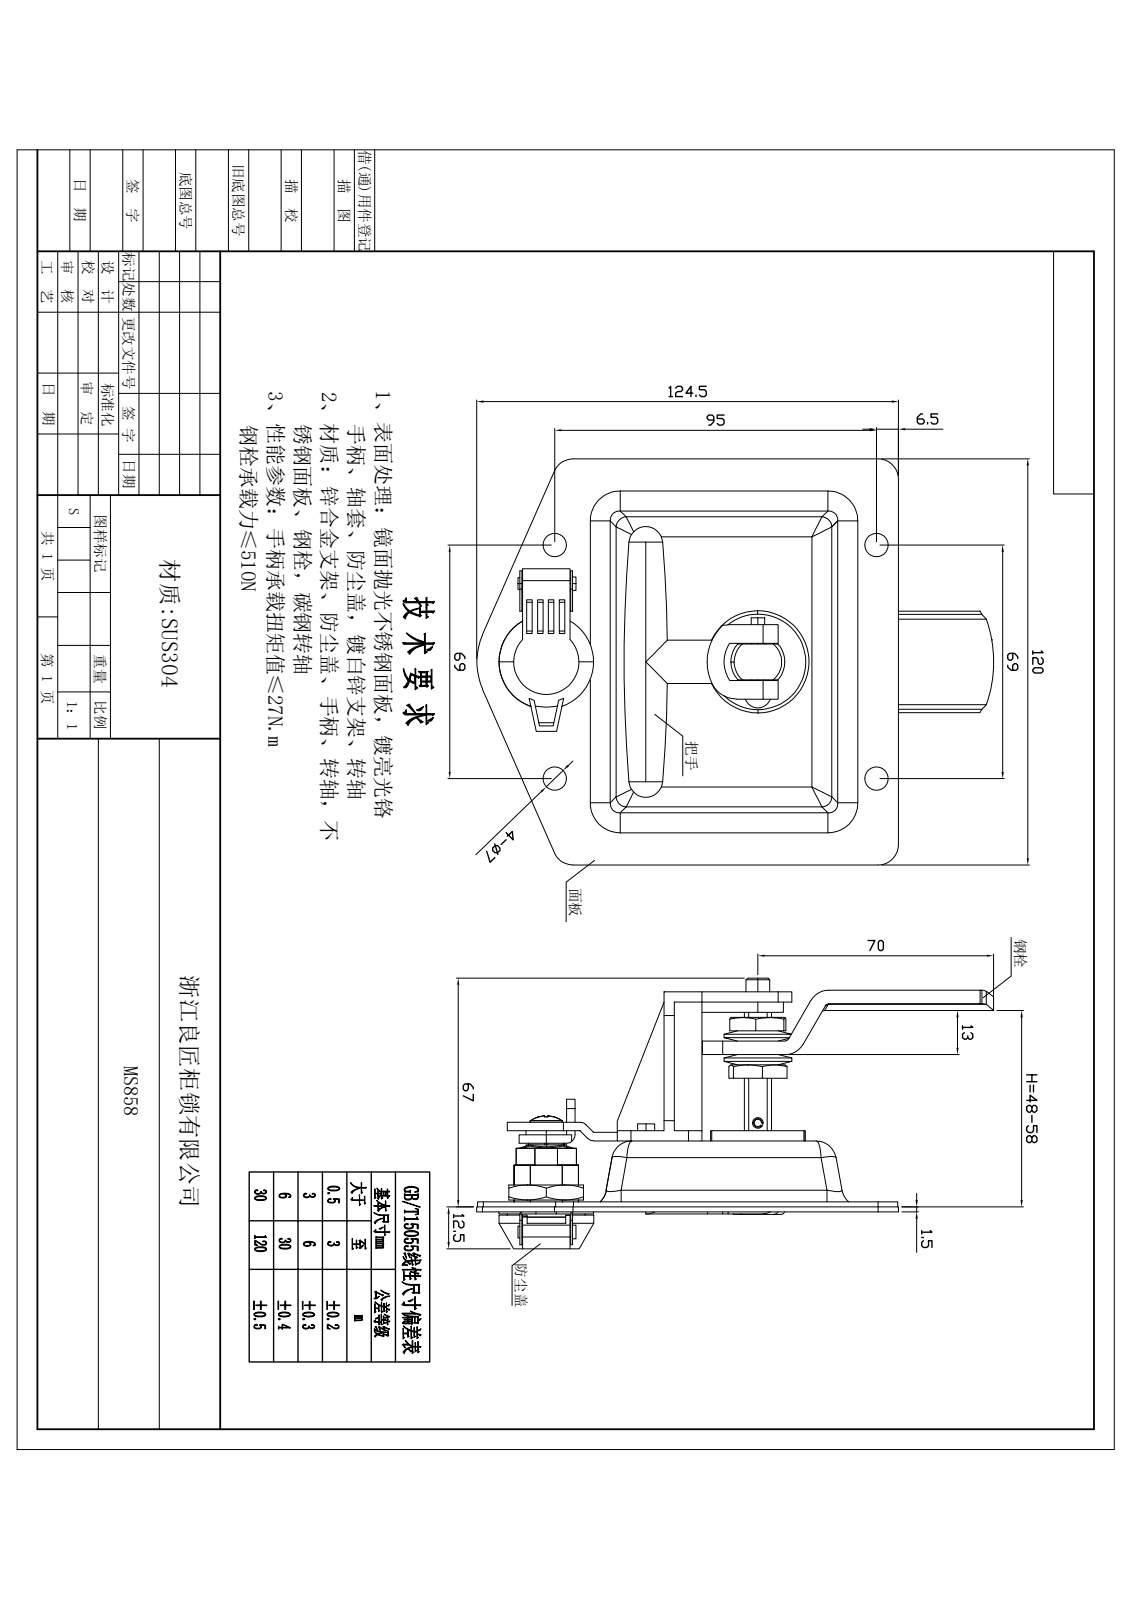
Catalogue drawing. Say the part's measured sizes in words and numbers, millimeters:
Its 3-D file was written by "Rhino 8.5 (CONFIG_CONTROL_DESIGN)". It is 22 solids with 833 faces: 402 planar, 328 cylindrical and 103 other. Overall it measures 152.6 by 120 by 80 millimeters. Its volume is 34 978 cubic millimeters and its surface area 89 366 square millimeters. Round holes: 5 of diameter 7.2, 4 of diameter 7, 2 of diameter 4, 2 of diameter 5.1, 1 of diameter 2.2, 1 of diameter 2.7, 1 of diameter 3, 1 of diameter 3.1, 1 of diameter 4.1, 1 of diameter 4.2, 1 of diameter 4.3, 1 of diameter 6. Round bosses or shafts: 3 of diameter 5, 2 of diameter 28, 2 of diameter 16, 2 of diameter 4, 1 of diameter 30.2, 1 of diameter 26, 1 of diameter 23, 1 of diameter 20. Partial cylindrical surfaces (rounded edges, fillets, slot ends): 22 of radius 6, 10 of radius 1.5, 8 of radius 5, 6 of radius 4.5, 5 of radius 3, 4 of radius 0.3, 4 of radius 1, 4 of radius 4. The main face-to-face distances are 3, 1.5, 21, 19.5, 18, 16.5, 4.5, 24, 62, 41. The hole center spacings are 34.59, 69, 27.55, 41.33, 41.37, 43.93, 49.15, 68.22.
